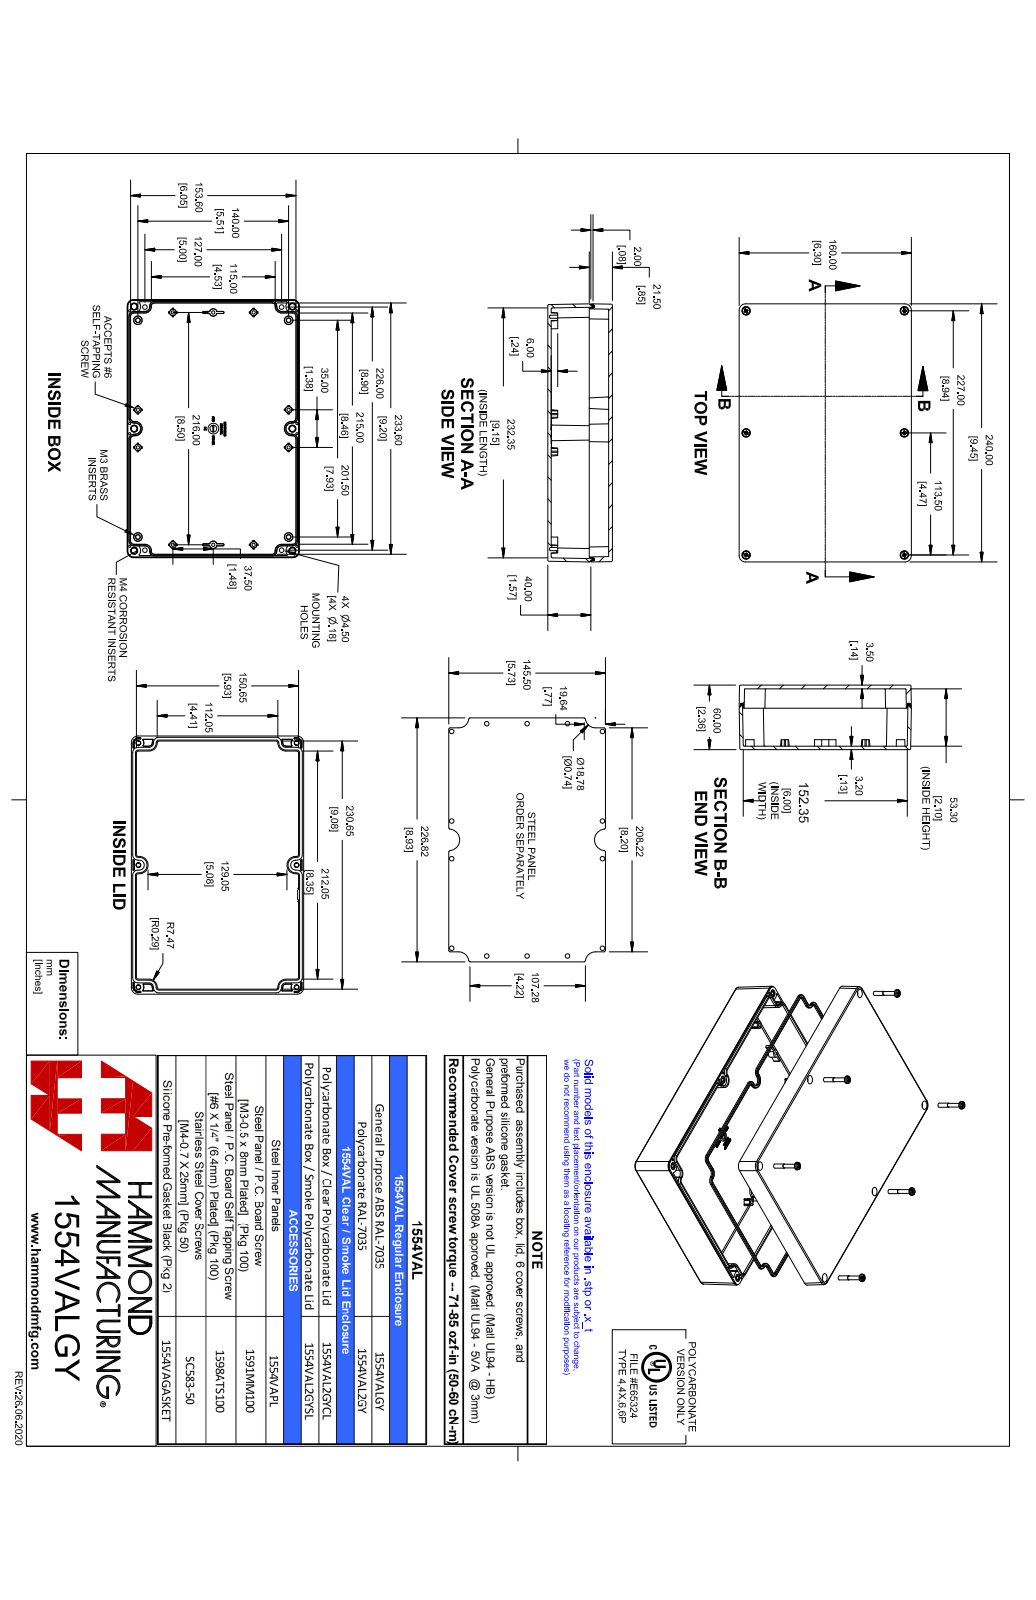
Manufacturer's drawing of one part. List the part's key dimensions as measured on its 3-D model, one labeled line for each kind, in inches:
Part name (STEP PRODUCT): 1554VALGY
STEP written by: SolidWorks 2021 (AUTOMOTIVE_DESIGN)
Units: inches
Bodies: 19 solids, 2046 faces (692 planar, 434 cylindrical, 920 other)
Overall size (bounding box): 9.449 × 6.299 × 2.362
Volume: 26.6 in³ · Surface area: 432.8 in²
Round holes (diameter × count): ⌀0.128 ×6, ⌀0.097 ×4, ⌀0.181 ×4
Round bosses / shafts (diameter × count): ⌀0.272 ×6, ⌀0.25 ×6, ⌀0.218 ×6, ⌀0.21 ×6, ⌀0.152 ×6, ⌀0.137 ×6, ⌀0.19 ×4, ⌀0.154 ×4
Partial cylindrical surfaces — rounded edges, fillets, slot ends (radius × count): R0.02 ×33, R0.012 ×28, R0.039 ×24, R0.1 ×12, R0.195 ×12, R0.236 ×8, R0.031 ×6, R0.059 ×4
Main face-to-face distances: 0.126, 2.362, 0.138, 2.224, 2.098, 2.236, 0.185, 6.299, 6.173, 6.114
Hole centre spacings: 0.52, 3.969, 4.469, 5.672, 6.903, 7.312, 8.436, 10.152
